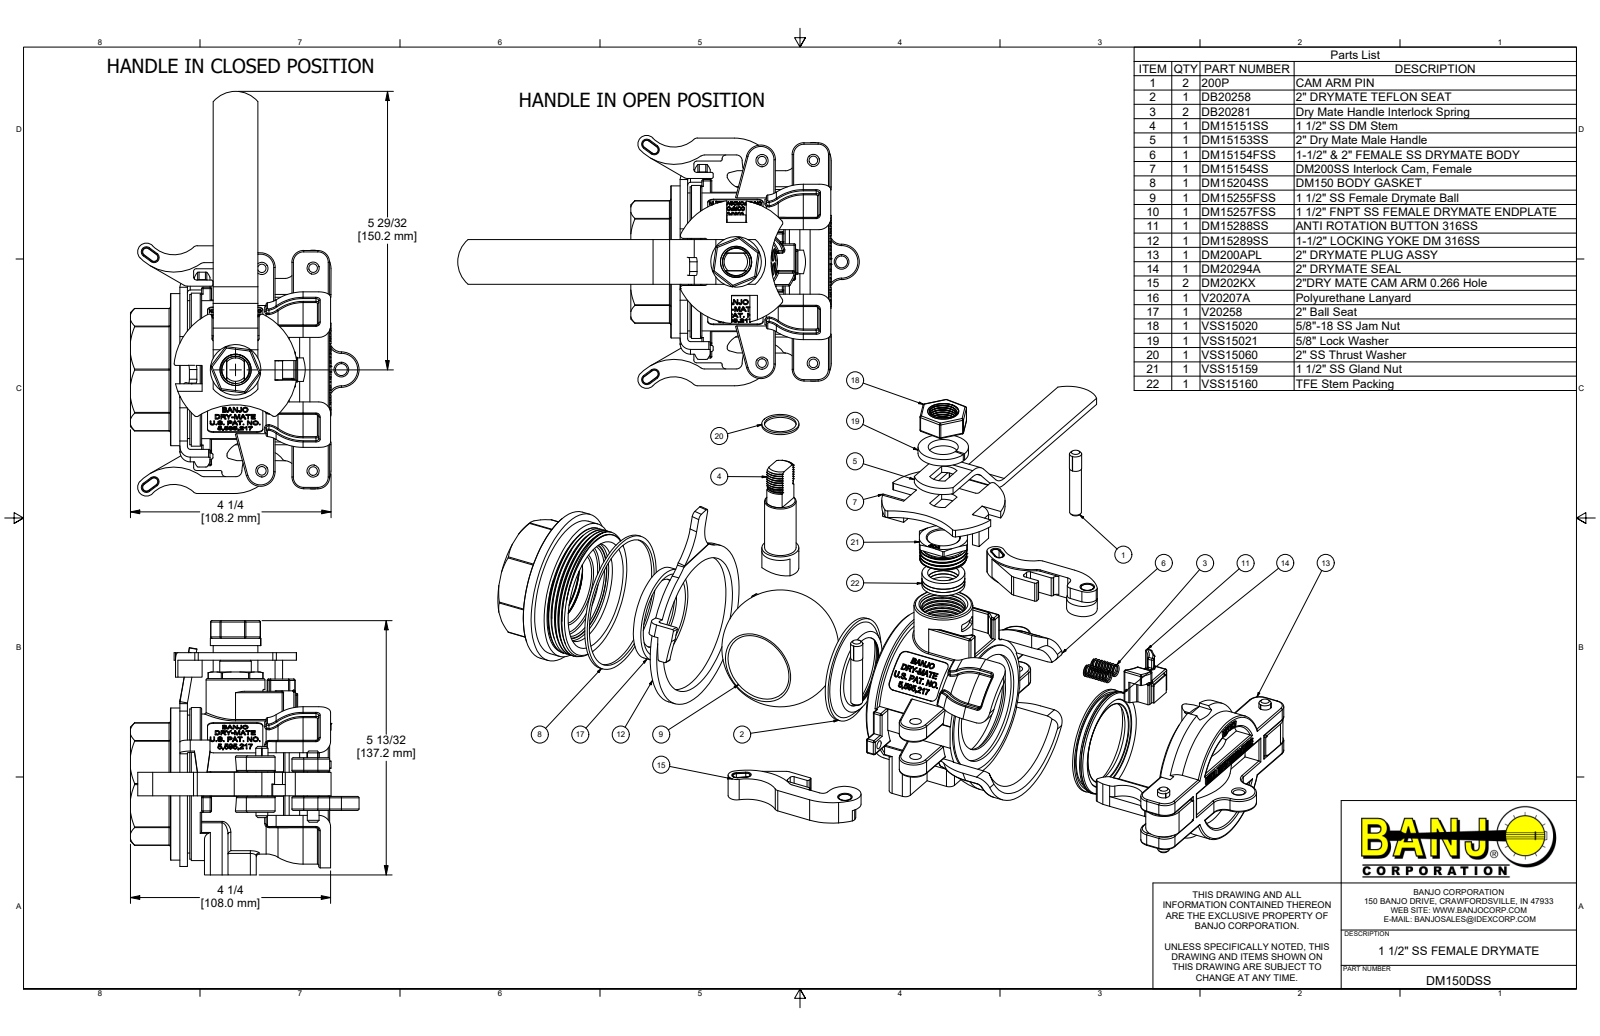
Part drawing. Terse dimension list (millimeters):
name: DM150DSS; DM15154FSS; DB20258; DB20281 (+8 more)
written by: Autodesk Inventor 2017 (AUTOMOTIVE_DESIGN)
unit: mm
bodies: 35 solids, 2811 faces (1146 planar, 638 cylindrical, 1027 other)
size: 346.32 × 150.25 × 137.3
volume: 479 096 mm³; area: 217 432 mm²
holes: 5× ⌀6.35, 4× ⌀6.5, 3× ⌀3.17, 2× ⌀38.1, 1× ⌀4.57, 1× ⌀14.73, 1× ⌀16.26, 1× ⌀16.82, 1× ⌀17.02, 1× ⌀17.17, 1× ⌀17.53, 1× ⌀21.34
bosses: 4× ⌀6.6, 4× ⌀6.32, 3× ⌀7.11, 1× ⌀88.9, 1× ⌀82.04, 1× ⌀81.03, 1× ⌀75.56, 1× ⌀75.44
rounds: 175× R0.76, 25× R1.52, 14× R3.17, 10× R3.05, 10× R6.35, 9× R2.03, 6× R0.81, 6× R25.4
face distances: 7.57, 4.07, 21.59, 3.81, 42.67, 55.37, 21.84, 21.85, 7.87, 20.57
hole spacings: 24.13, 27.68, 41.8, 56.43, 56.82, 57.12, 68.92, 69.46
